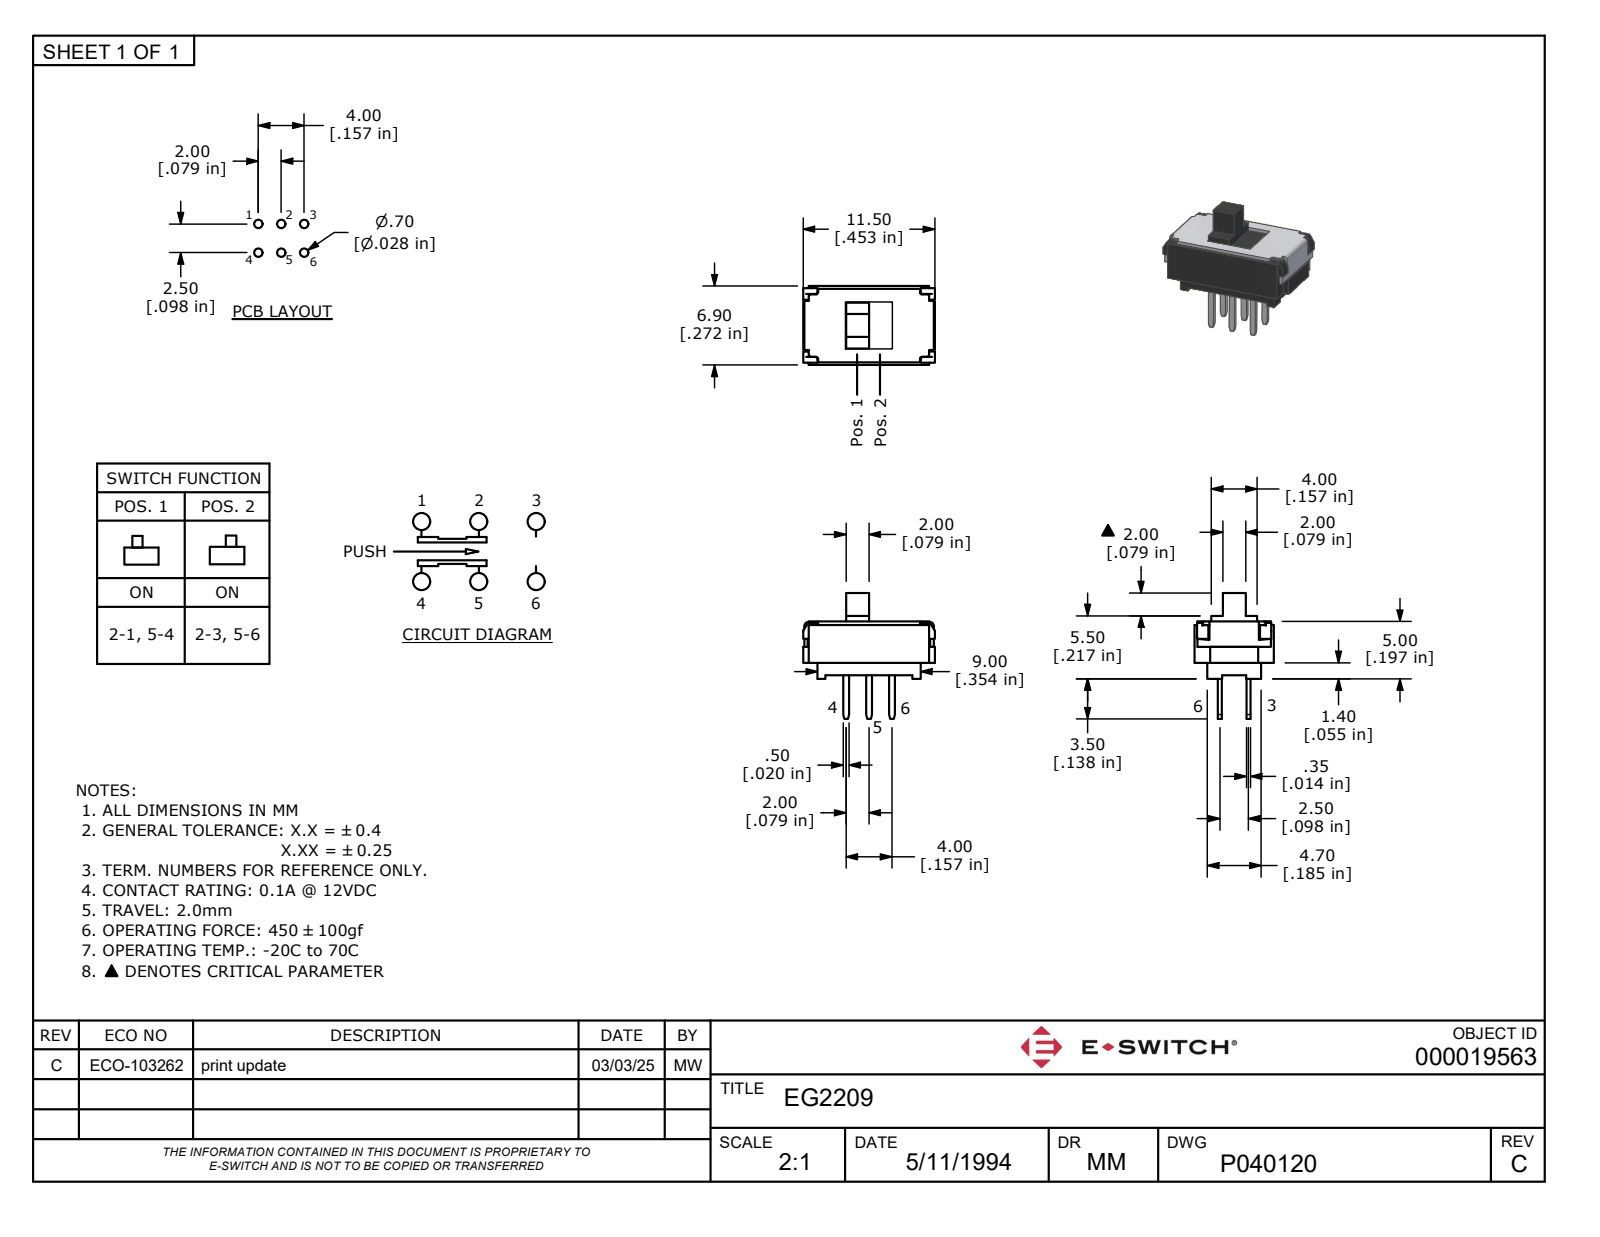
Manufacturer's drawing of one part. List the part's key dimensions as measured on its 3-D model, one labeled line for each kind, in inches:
Part name (STEP PRODUCT): 000019563_Simplify_1
STEP written by: Autodesk Inventor 2022 (AUTOMOTIVE_DESIGN)
Units: inches
Bodies: 1 solid, 201 faces (173 planar, 28 cylindrical, 0 other)
Overall size (bounding box): 0.453 × 0.433 × 0.272
Volume: 0.02 in³ · Surface area: 0.688 in²
Partial cylindrical surfaces — rounded edges, fillets, slot ends (radius × count): R0.006 ×18, R0.004 ×2, R0.016 ×2
Main face-to-face distances: 0.043, 0.185, 0.142, 0.272, 0.433, 0.016, 0.098, 0.079, 0.02, 0.228
